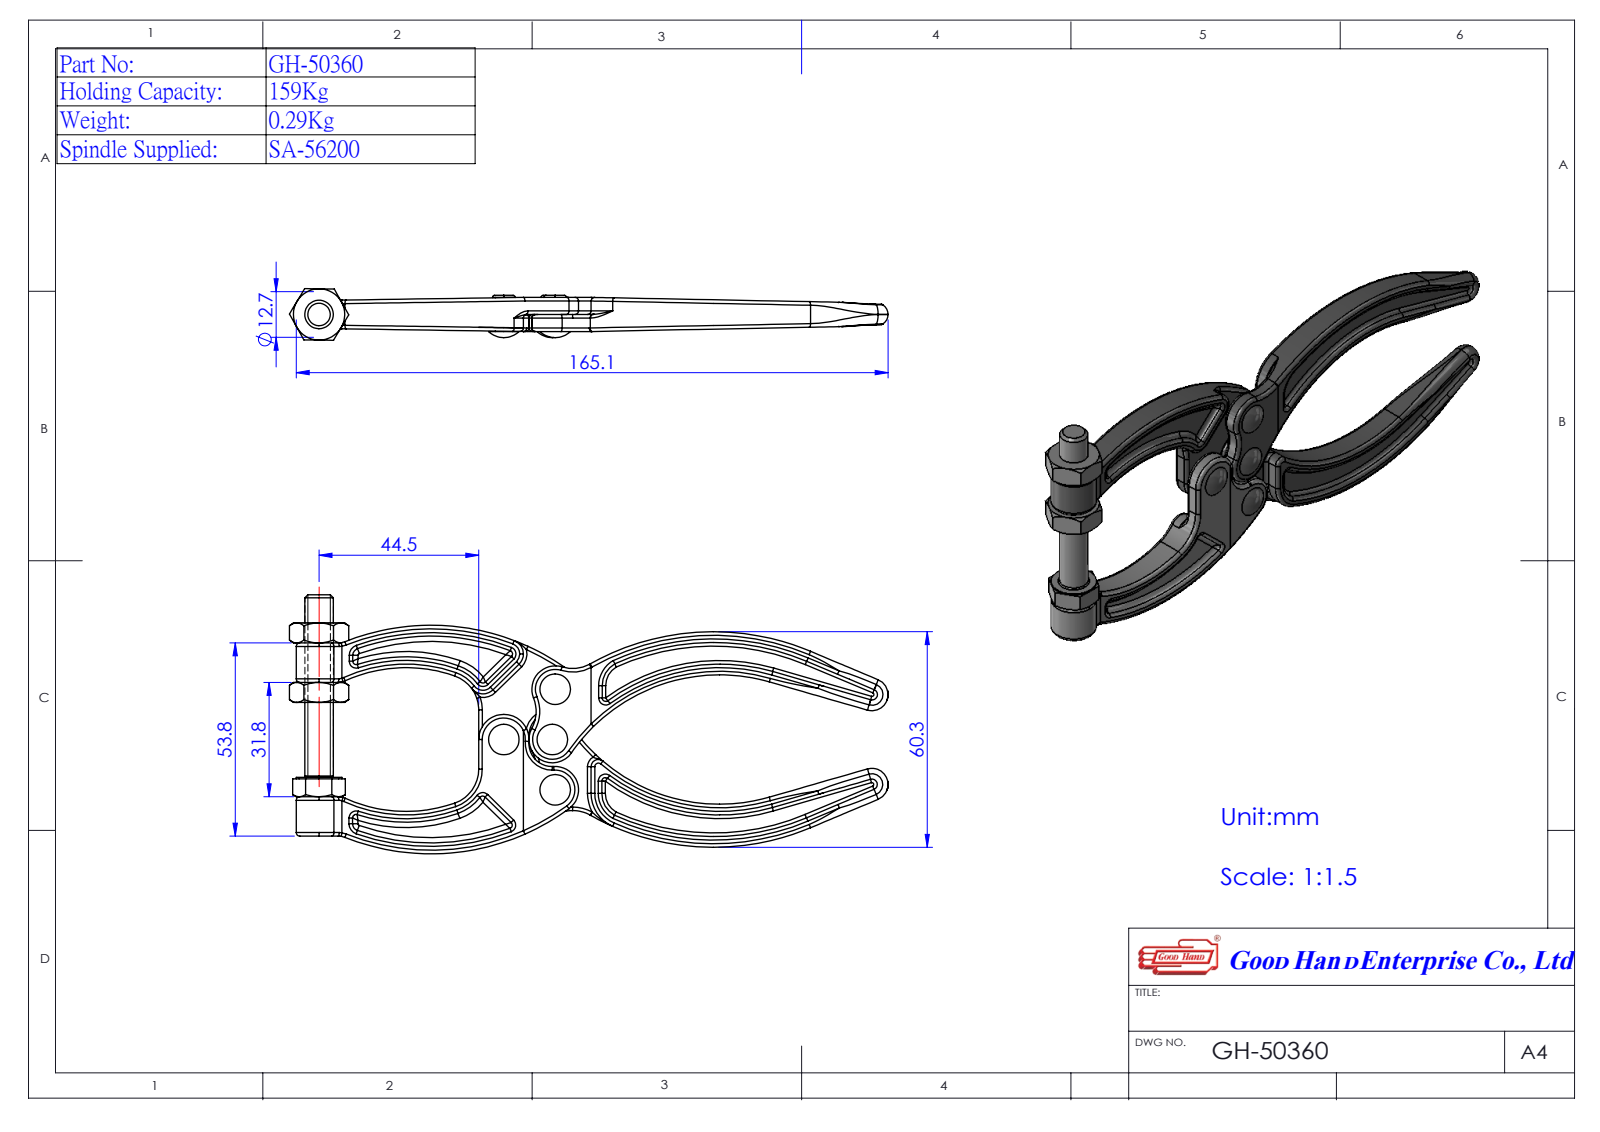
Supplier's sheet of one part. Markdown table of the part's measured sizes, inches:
| quantity | value |
| --- | --- |
| part name | Group2^493800(GH-50360); Group1^493800(GH-50360); Group3^493800(GH-50360); 35036001-2^493800(GH-50360) (+1 more) |
| STEP written by | SolidWorks 2016 (AUTOMOTIVE_DESIGN) |
| units | inches |
| bodies | 4 solids, 279 faces (97 planar, 94 cylindrical, 88 other) |
| overall size | 6.561 × 2.837 × 0.567 |
| volume | 2.254 in³ |
| surface area | 33.85 in² |
| round holes (diameter × count) | 0.118 × 4 |
| round bosses / shafts (diameter × count) | 0.551 × 1, 0.512 × 1, 0.5 × 1, 0.313 × 1, 0.189 × 1 |
| partial cylindrical surfaces (radius × count) | 0.394 × 8, 0.039 × 4, 0.079 × 4, 0.157 × 4, 0.256 × 4, 0.129 × 2, 0.177 × 2, 0.512 × 2 |
| main face-to-face distances | 0.187, 0.077, 0.078, 0.079, 0.079, 0.374, 0.031, 0.432, 1.464, 1.032 |
| hole center spacings | 0.552, 0.788, 0.531, 1.102 |
